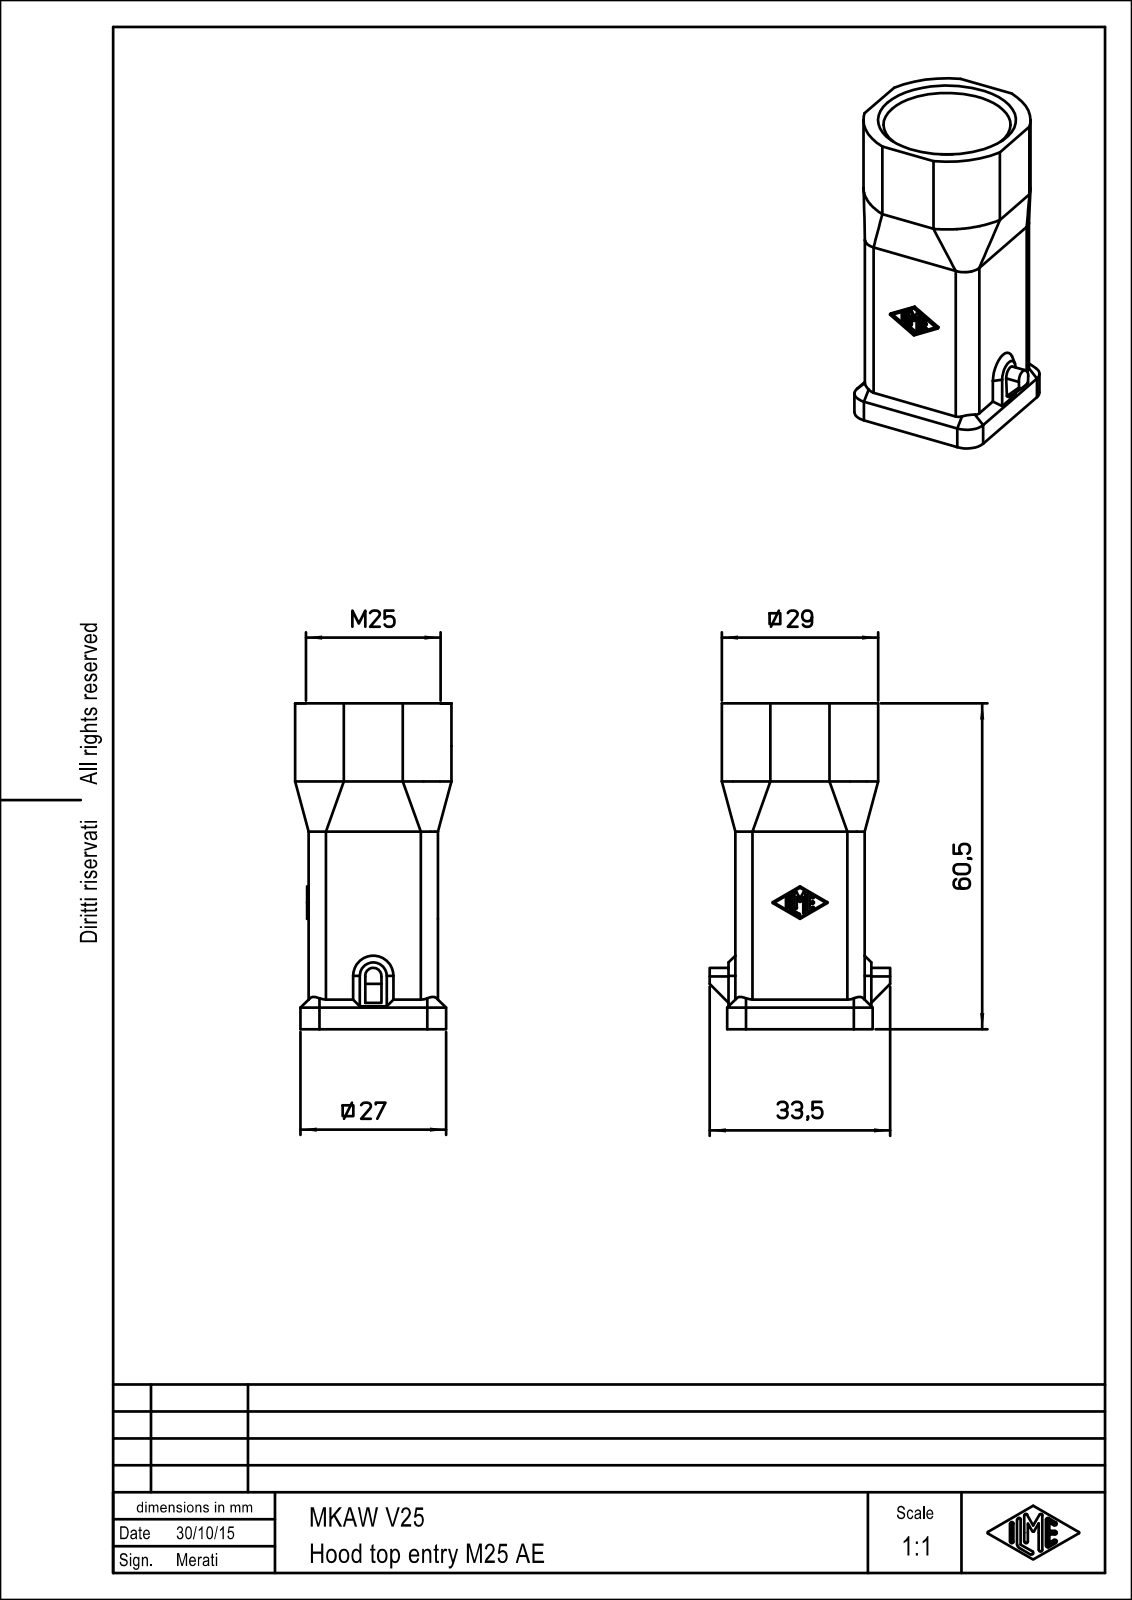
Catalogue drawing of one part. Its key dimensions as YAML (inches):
part_name: "MKA_V25_54215"
step_written_by: "PTC Creo Elements/Direct Modeling 19.0B 21-Mar-2015 (C) Parametric Technology GmbH (AUTOMOTIVE_DESIGN)"
units: inches
bodies: {solids: 1, faces: 283, planar: 216, cylindrical: 52, other: 15}
overall_size: [2.382, 1.319, 1.154]
volume: 0.656
surface_area: 18.02
round_holes:
  - {diameter: 0.126, count: 1}
  - {diameter: 0.276, count: 1}
  - {diameter: 0.787, count: 1}
  - {diameter: 0.929, count: 1}
partial_cylinders:
  - {radius: 0.008, count: 11}
  - {radius: 0.079, count: 8}
  - {radius: 0.126, count: 4}
  - {radius: 0.138, count: 4}
  - {radius: 0.004, count: 3}
  - {radius: 0.006, count: 2}
  - {radius: 0.069, count: 2}
  - {radius: 0.098, count: 2}
face_to_face_distances: [0.047, 0.898, 0.85, 0.945, 0.059, 1.043, 0.098, 0.957, 0.146, 0.996]
